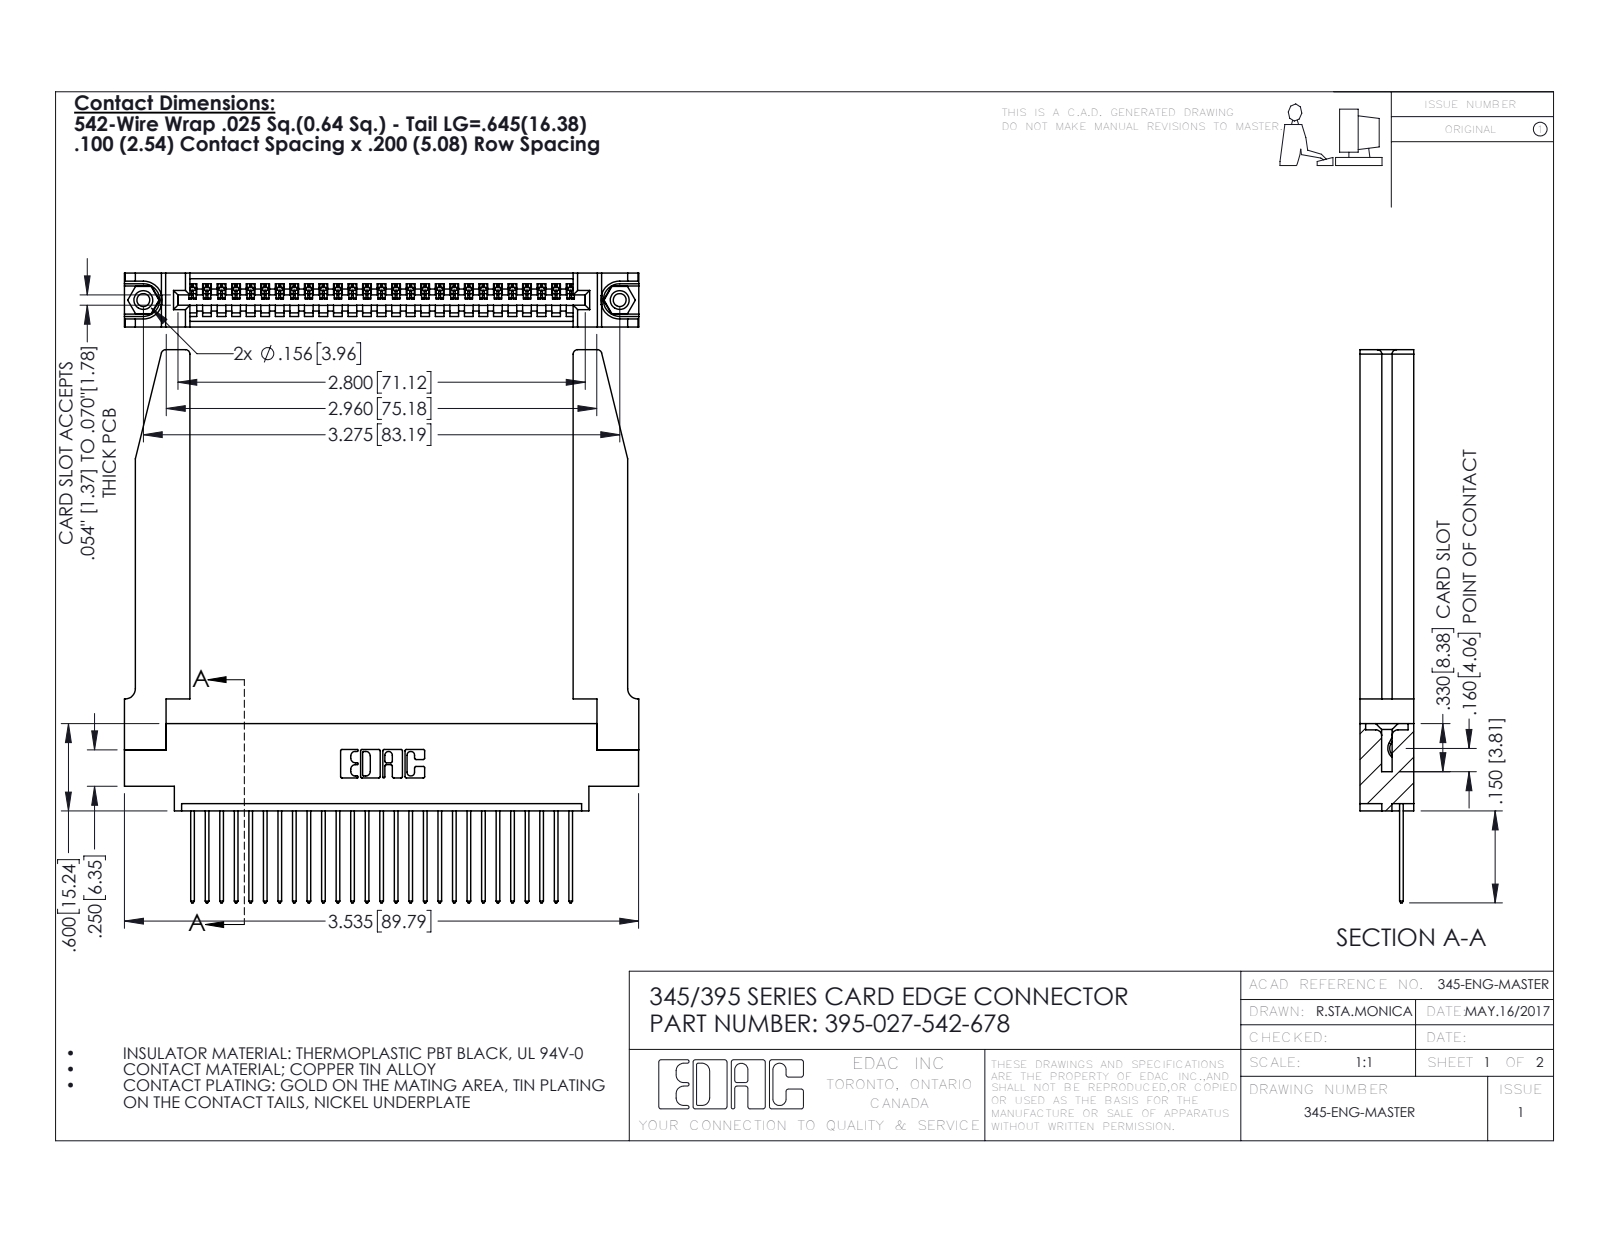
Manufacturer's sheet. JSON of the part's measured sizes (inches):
{"part_name": "345 Part_0.170 Offset - 0.156 Dia-TH; 345-220-078_345-220-078; 345-250-001_345-250-001-102; 395-027-542-678 (+1 more)", "step_written_by": "SolidWorks 2016 (CONFIG_CONTROL_DESIGN)", "units": "inches", "bodies": {"solids": 32, "faces": 1930, "planar": 1306, "cylindrical": 572, "other": 52}, "overall_size": [3.802, 3.536, 0.37], "volume_in3": 0.984, "surface_area_in2": 28.29, "round_holes": [[0.089, 2], [0.125, 2], [0.156, 2], [0.064, 1]], "round_bosses_or_shafts": [[0.155, 2]], "partial_cylinders_radius": [[0.006, 54], [0.01, 54], [0.01, 22], [0.03, 8], [0.007, 6], [0.031, 6], [0.026, 3], [0.031, 2]], "face_to_face_distances": [0.37, 0.072, 0.298, 0.098, 0.272, 0.025, 0.2, 0.148, 0.15, 0.225], "hole_center_spacings": [0.27, 3.04, 3.275]}
